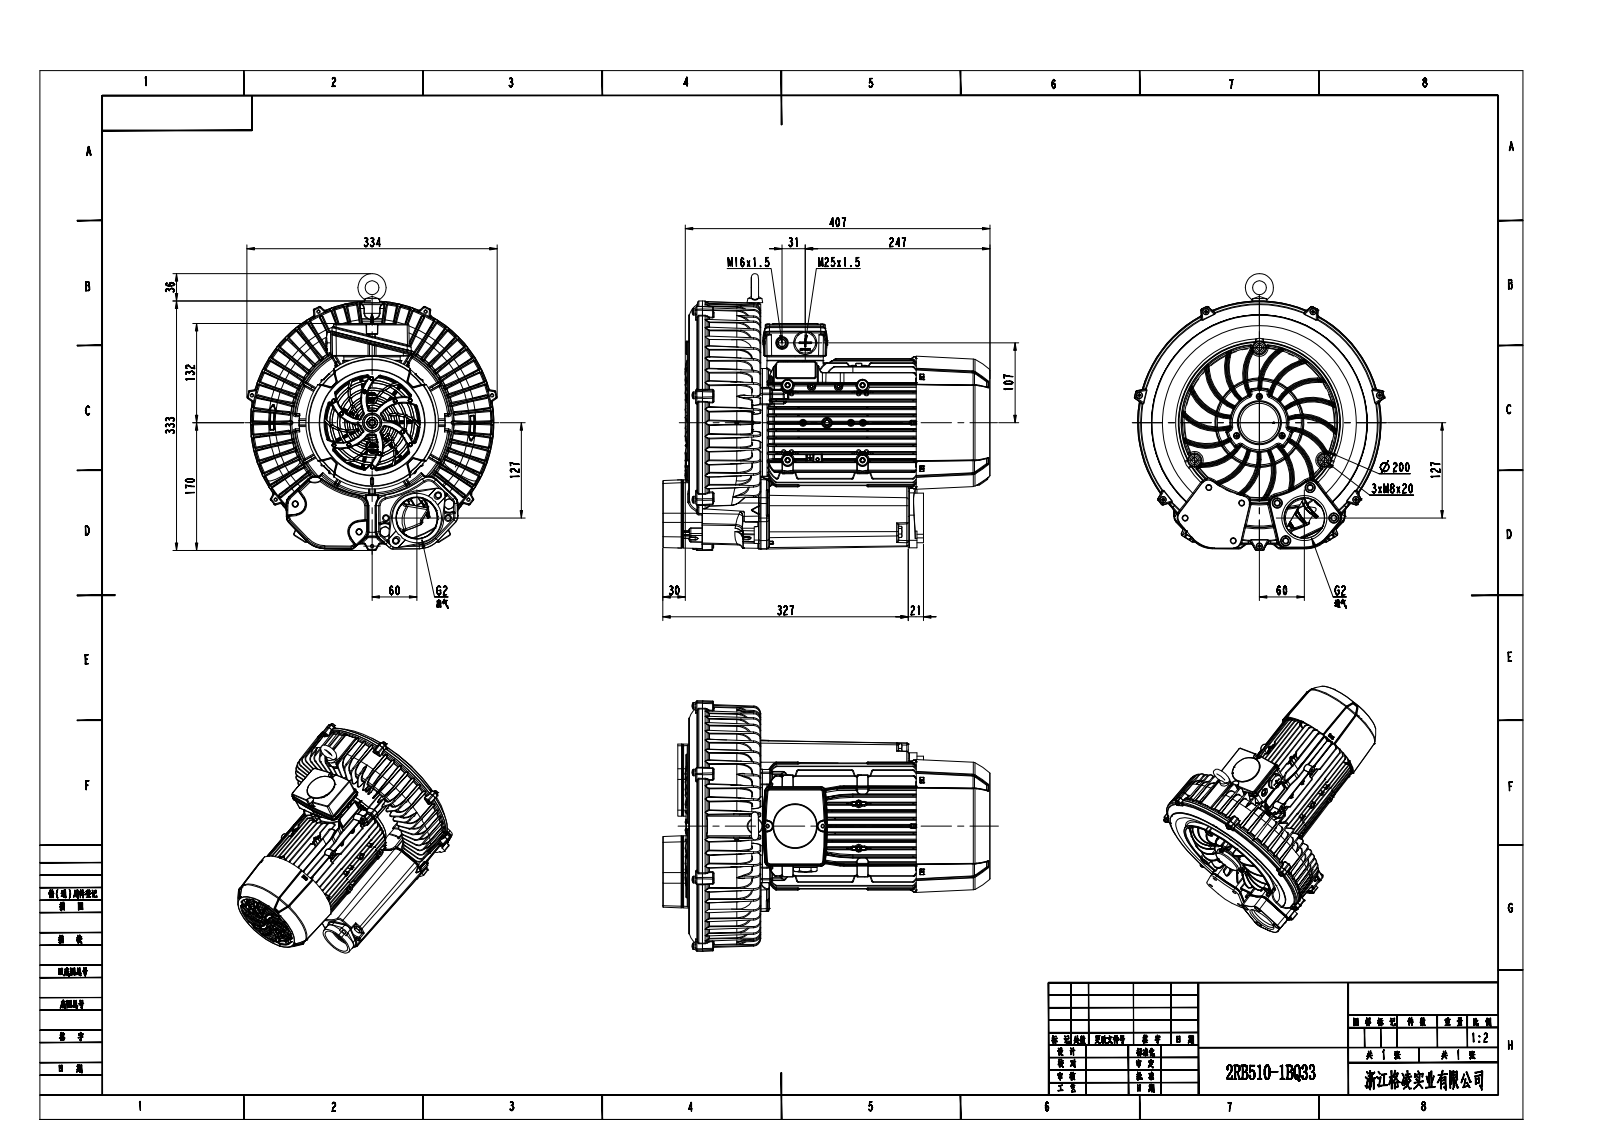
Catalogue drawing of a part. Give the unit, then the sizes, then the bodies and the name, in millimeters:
Units: millimetres
Overall size (bounding box): 436.7 × 368.92 × 340
Round holes (diameter × count): ⌀6.8 ×3, ⌀54.11 ×1, ⌀56.5 ×1
Round bosses / shafts (diameter × count): ⌀340 ×1, ⌀177 ×1, ⌀66.3 ×1
Partial cylindrical surfaces — rounded edges, fillets, slot ends (radius × count): R4.25 ×4, R7 ×4, R10 ×4, R11 ×4, R14 ×4, R7.5 ×2, R9 ×2, R9.99 ×2
Main face-to-face distances: 100, 306.2, 406.2, 11.6, 294.6, 111.6, 416.7, 122.1, 110.5, 10.5
Hole centre spacings: 173.2, 81.47, 165.59, 234.8, 120
Volume: 18 860 000 mm³ · Surface area: 574 529 mm²
Bodies: 1 solid, 123 faces (59 planar, 54 cylindrical, 10 other)
Part name (STEP PRODUCT): 2RB510-1AQ36
STEP written by: PRO/ENGINEER BY PARAMETRIC TECHNOLOGY CORPORATION, 2007090 (AUTOMOTIVE_DESIGN_CC2)
